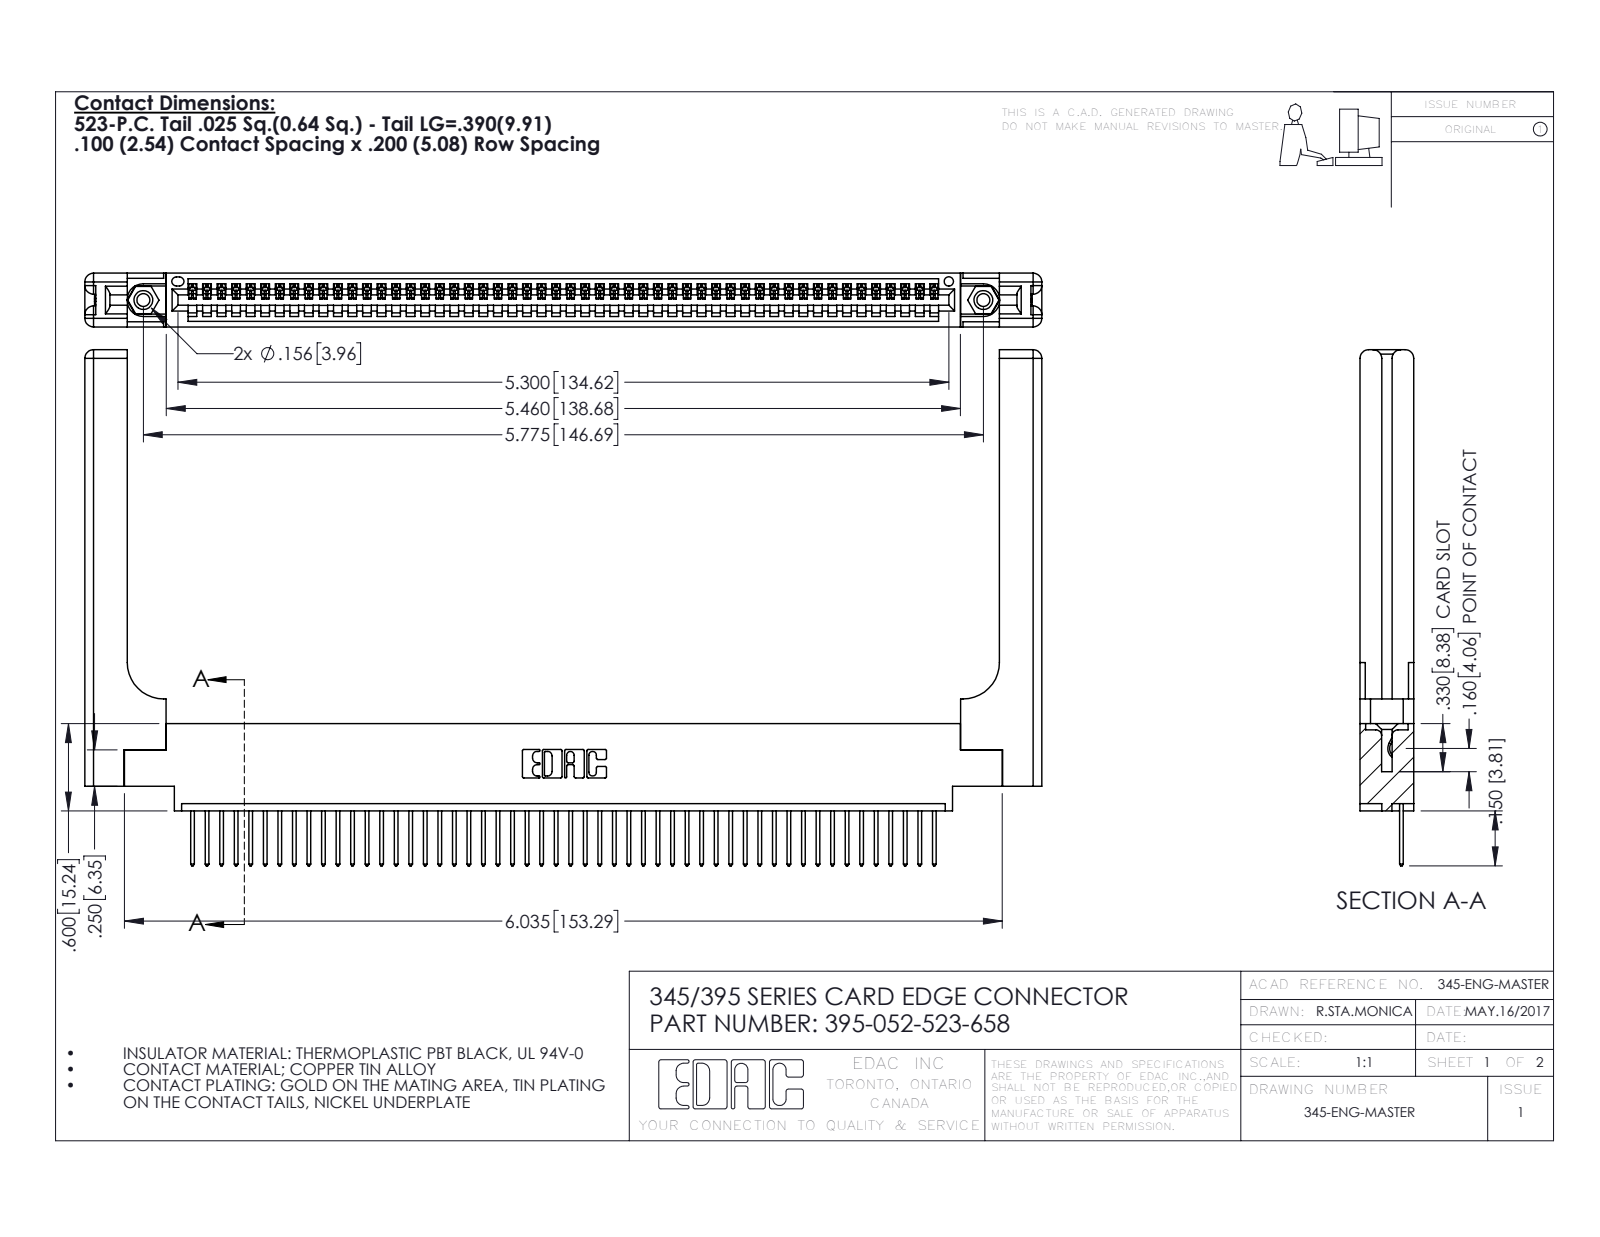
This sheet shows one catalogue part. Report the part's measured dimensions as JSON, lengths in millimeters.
{"part_name": "345-220-058_345-220-058; 395-052-523-658; 345-250-001_345-250-001-102; 345 Part_0.170 Offset - 0.156 Dia-TH (+1 more)", "step_written_by": "SolidWorks 2016 (CONFIG_CONTROL_DESIGN)", "units": "millimeters", "bodies": {"solids": 57, "faces": 3402, "planar": 2312, "cylindrical": 1030, "other": 60}, "overall_size": [167.1, 90.1, 9.4], "volume_mm3": 24320, "surface_area_mm2": 26650, "round_holes": [[2.3, 2], [3.2, 2], [4, 2], [1.6, 1]], "round_bosses_or_shafts": [[3.9, 2]], "partial_cylinders_radius": [[0.2, 104], [0.3, 104], [0.3, 22], [1.5, 16], [0.2, 6], [0.8, 6], [0.7, 3], [0.8, 2]], "face_to_face_distances": [1.8, 9.4, 7.6, 2.5, 6.9, 0.6, 5.1, 5.7, 3.8, 3.8], "hole_center_spacings": [6.9, 140.7, 146.7]}
